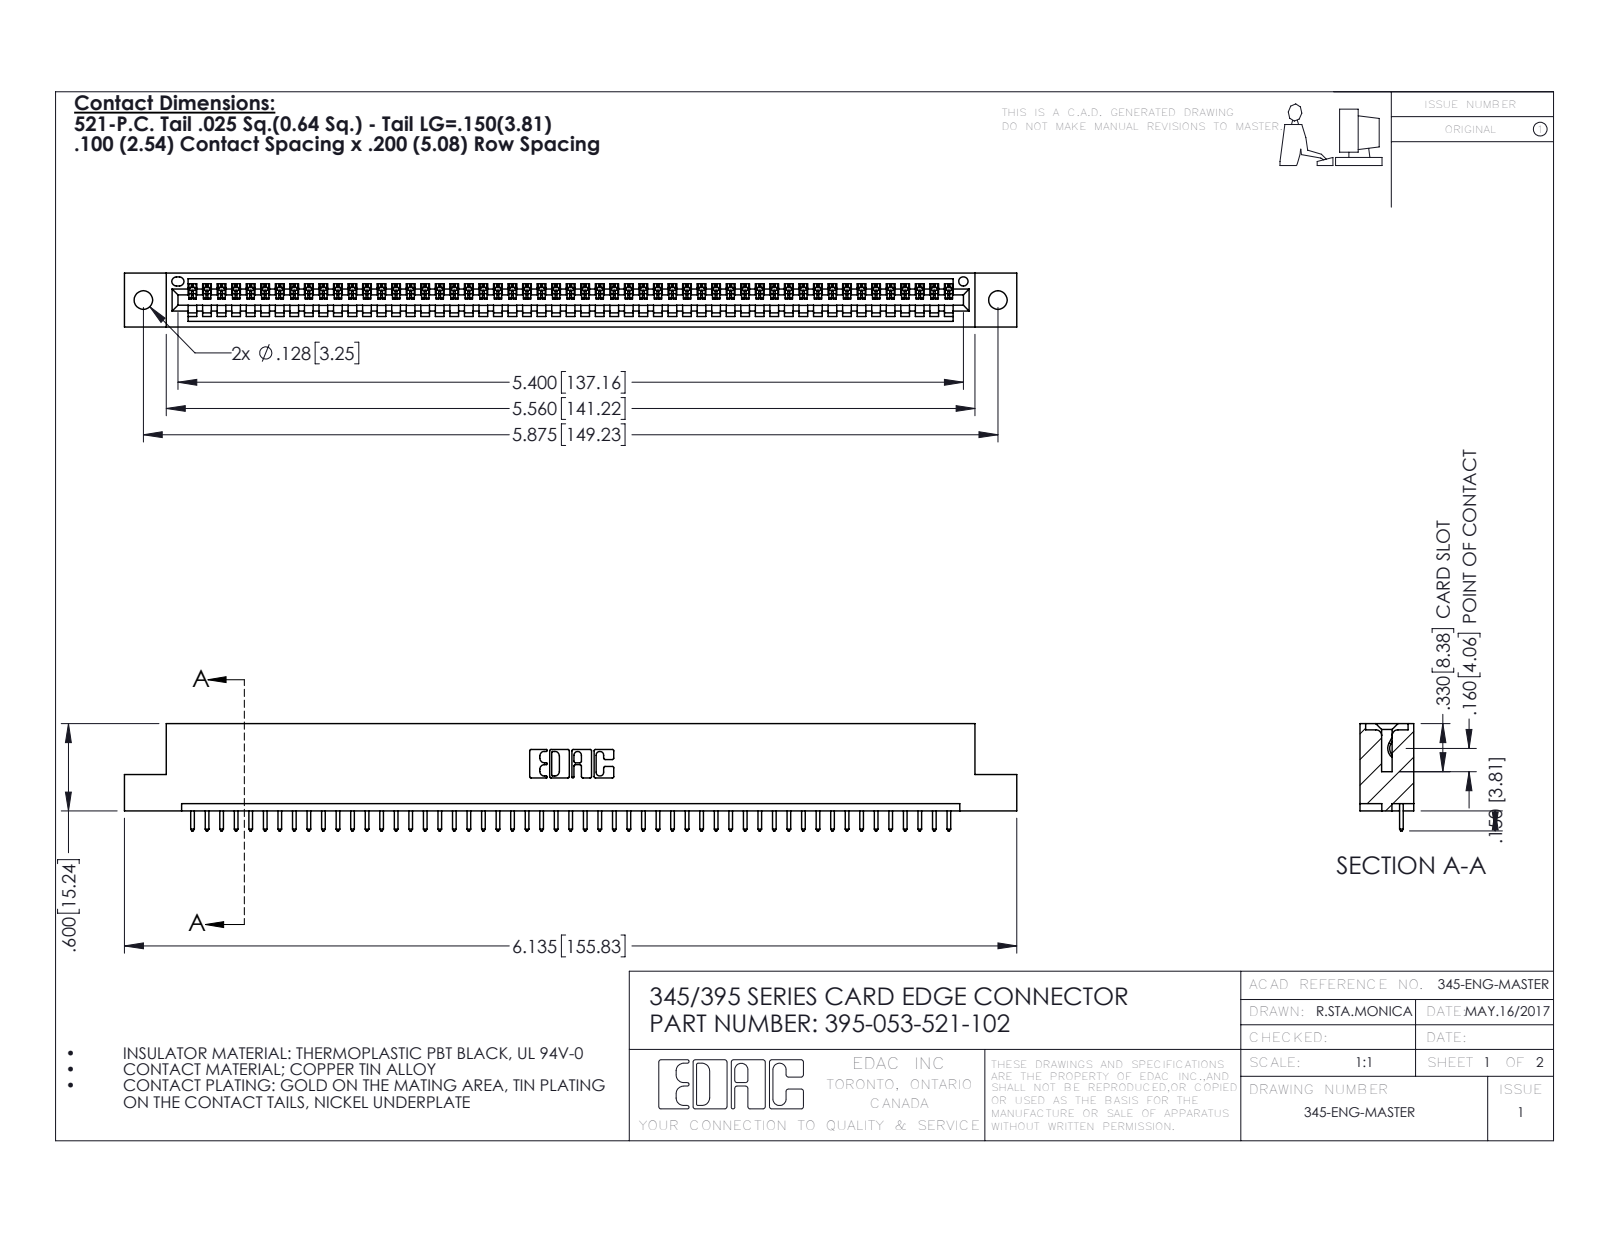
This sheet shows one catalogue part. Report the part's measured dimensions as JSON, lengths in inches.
{"part_name": "395-053-521-102; 345-292-001_345-293-121; 345 Part_Flush Mounting Lugs - 0.128 Dia", "step_written_by": "SolidWorks 2016 (CONFIG_CONTROL_DESIGN)", "units": "inches", "bodies": {"solids": 54, "faces": 3200, "planar": 2200, "cylindrical": 1000, "other": 0}, "overall_size": [6.135, 0.737, 0.37], "volume_in3": 0.897, "surface_area_in2": 29.18, "round_holes": [[0.128, 2], [0.064, 1]], "partial_cylinders_radius": [[0.006, 106], [0.01, 106], [0.01, 22], [0.007, 6], [0.031, 6], [0.026, 3], [0.031, 2], [0.04, 2]], "face_to_face_distances": [0.298, 0.072, 0.37, 0.2, 0.098, 0.272, 0.025, 0.225, 0.149, 0.072], "hole_center_spacings": [0.27, 5.639, 5.875]}
